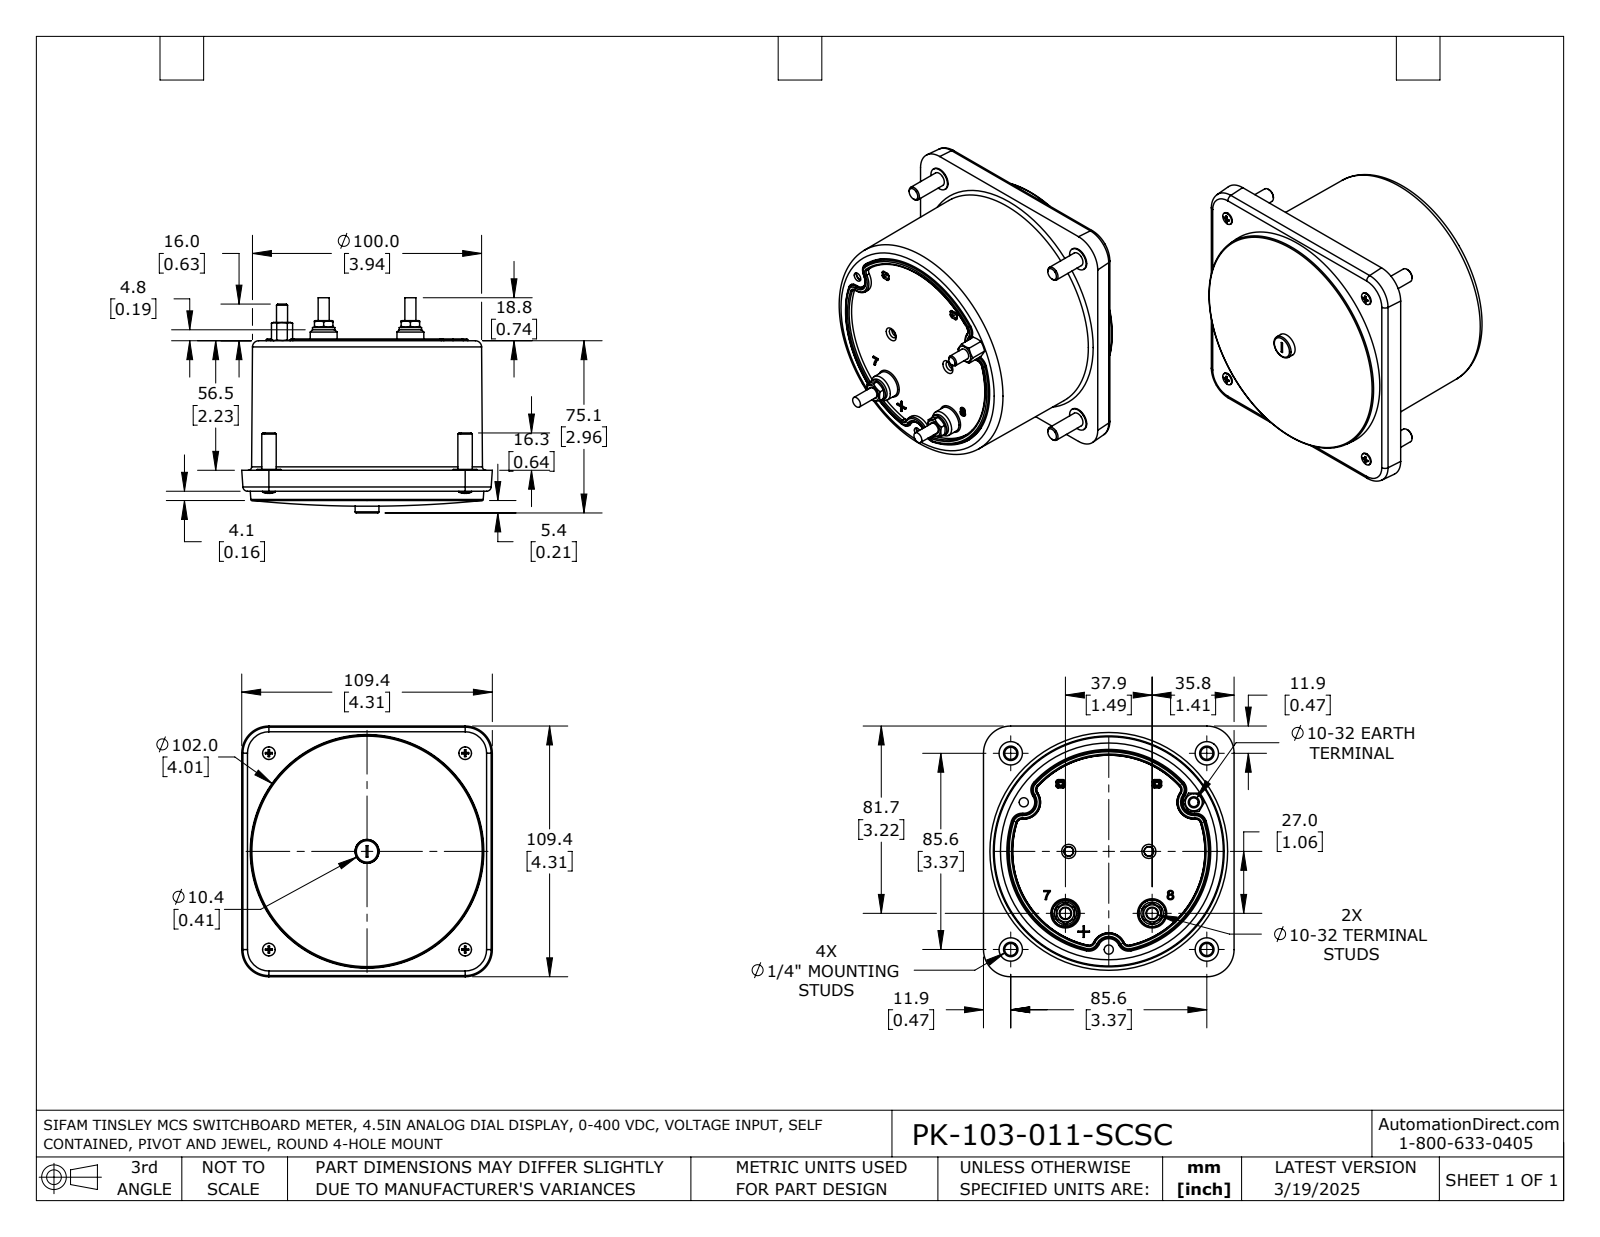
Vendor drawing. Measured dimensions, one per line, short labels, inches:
name: PK-103-011-SCSC
written by: SolidWorks 2021 (AUTOMOTIVE_DESIGN)
unit: in
bodies: 1 solid, 609 faces (167 planar, 141 cylindrical, 301 other)
size: 4.307 × 4.307 × 3.697
volume: 36.28 in³; area: 82.21 in²
holes: 4× ⌀0.094, 4× ⌀0.138, 4× ⌀0.315, 3× ⌀0.157, 2× ⌀0.209
bosses: 4× ⌀0.402, 4× ⌀0.248, 4× ⌀0.217, 4× ⌀0.114, 3× ⌀0.19, 2× ⌀0.384, 1× ⌀0.146
rounds: 24× R0.02, 9× R0.189, 4× R0.079, 1× R1.752
face distances: 2.177, 2.537, 0.36, 0.048, 2.225, 2.585, 0.489, 2.715, 2.667, 0.129
hole spacings: 3.372, 3.37, 3.374, 3.378, 3.38, 4.769, 0.971, 1.126
